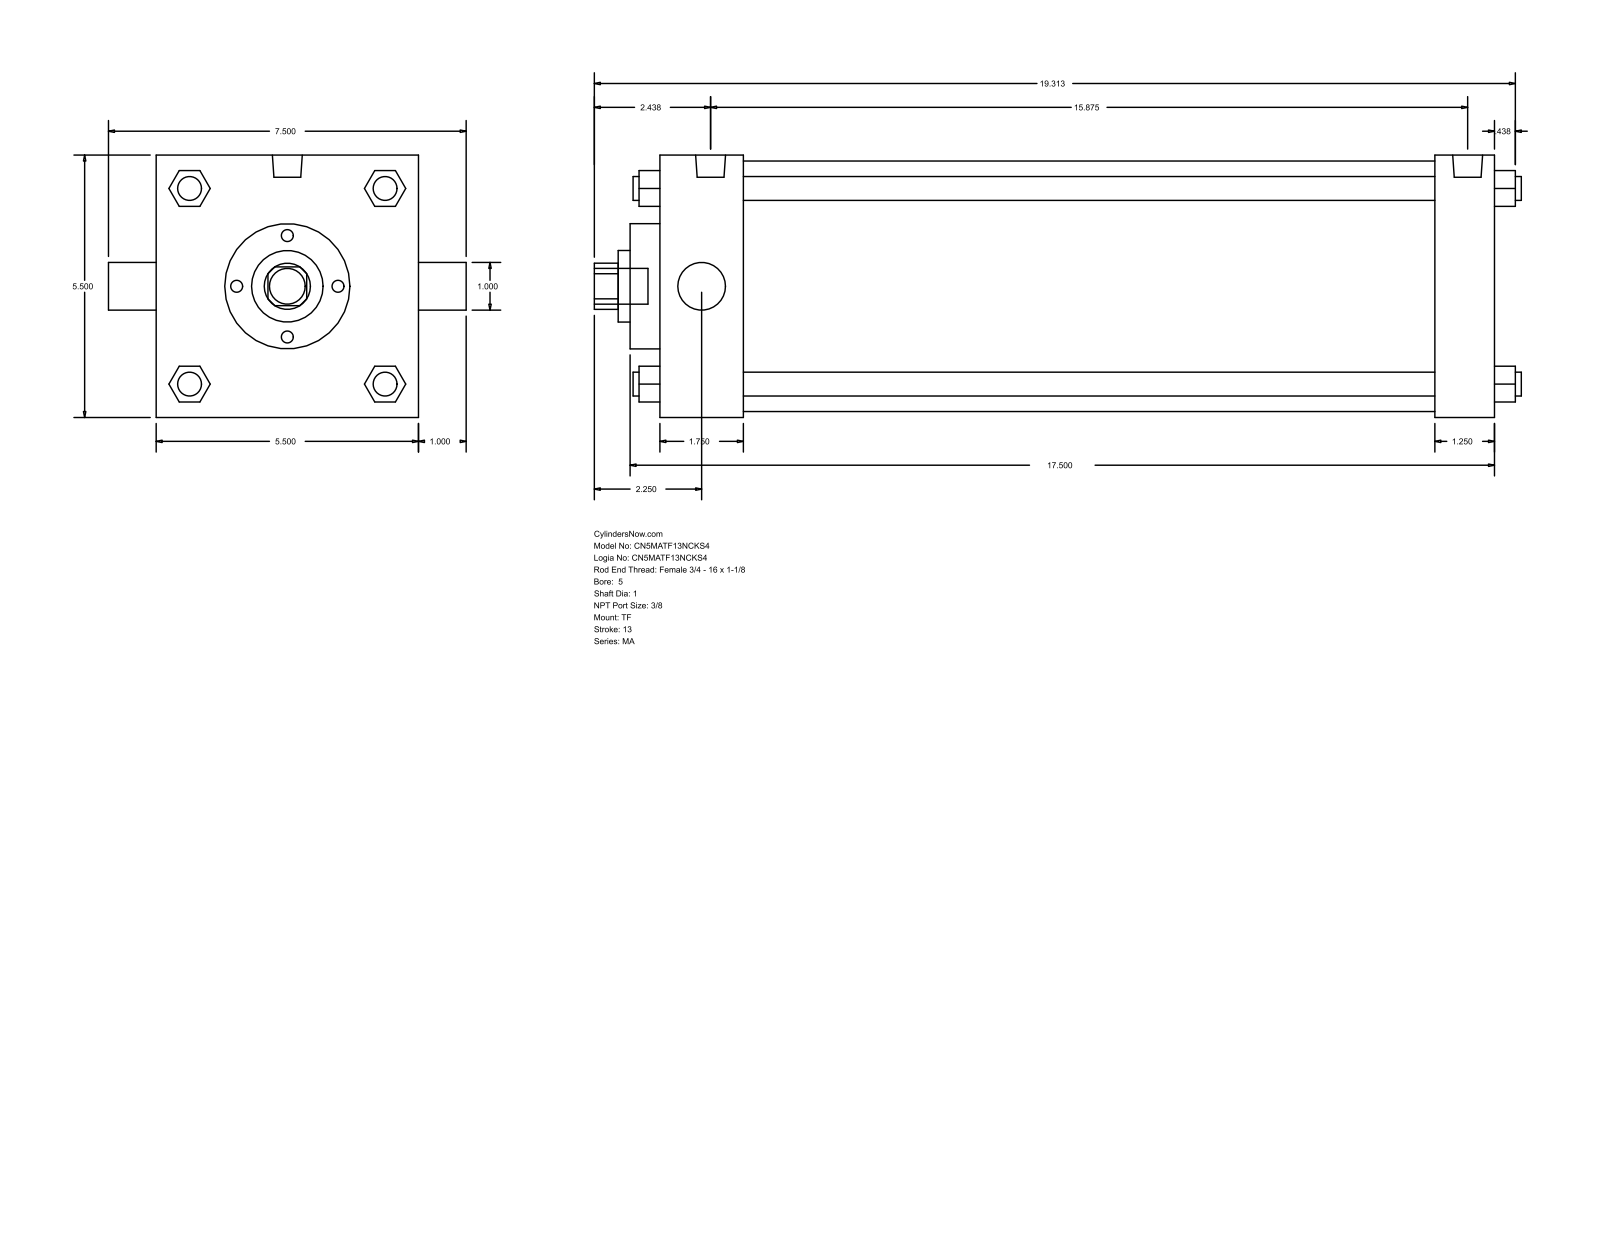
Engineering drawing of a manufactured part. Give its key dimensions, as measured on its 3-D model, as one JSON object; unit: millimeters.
{"part_name": "MA_TF__0500_1", "step_written_by": "GSSL Pune (CONFIG_CONTROL_DESIGN)", "units": "millimeters", "bodies": {"solids": 0, "faces": 122, "planar": 93, "cylindrical": 29, "other": 0}, "overall_size": [493.71, 190.5, 139.7], "round_holes": [[25.4, 2], [38.1, 1], [66.67, 1], [133.35, 1]], "round_bosses_or_shafts": [[12.7, 4], [11.11, 3], [15.93, 2], [19.05, 1]], "partial_cylinders_radius": [[12.29, 1]], "face_to_face_distances": [139.7, 444.51, 412.76, 31.75, 44.46, 368.3, 400.05, 15.87, 60.33, 428.63]}
